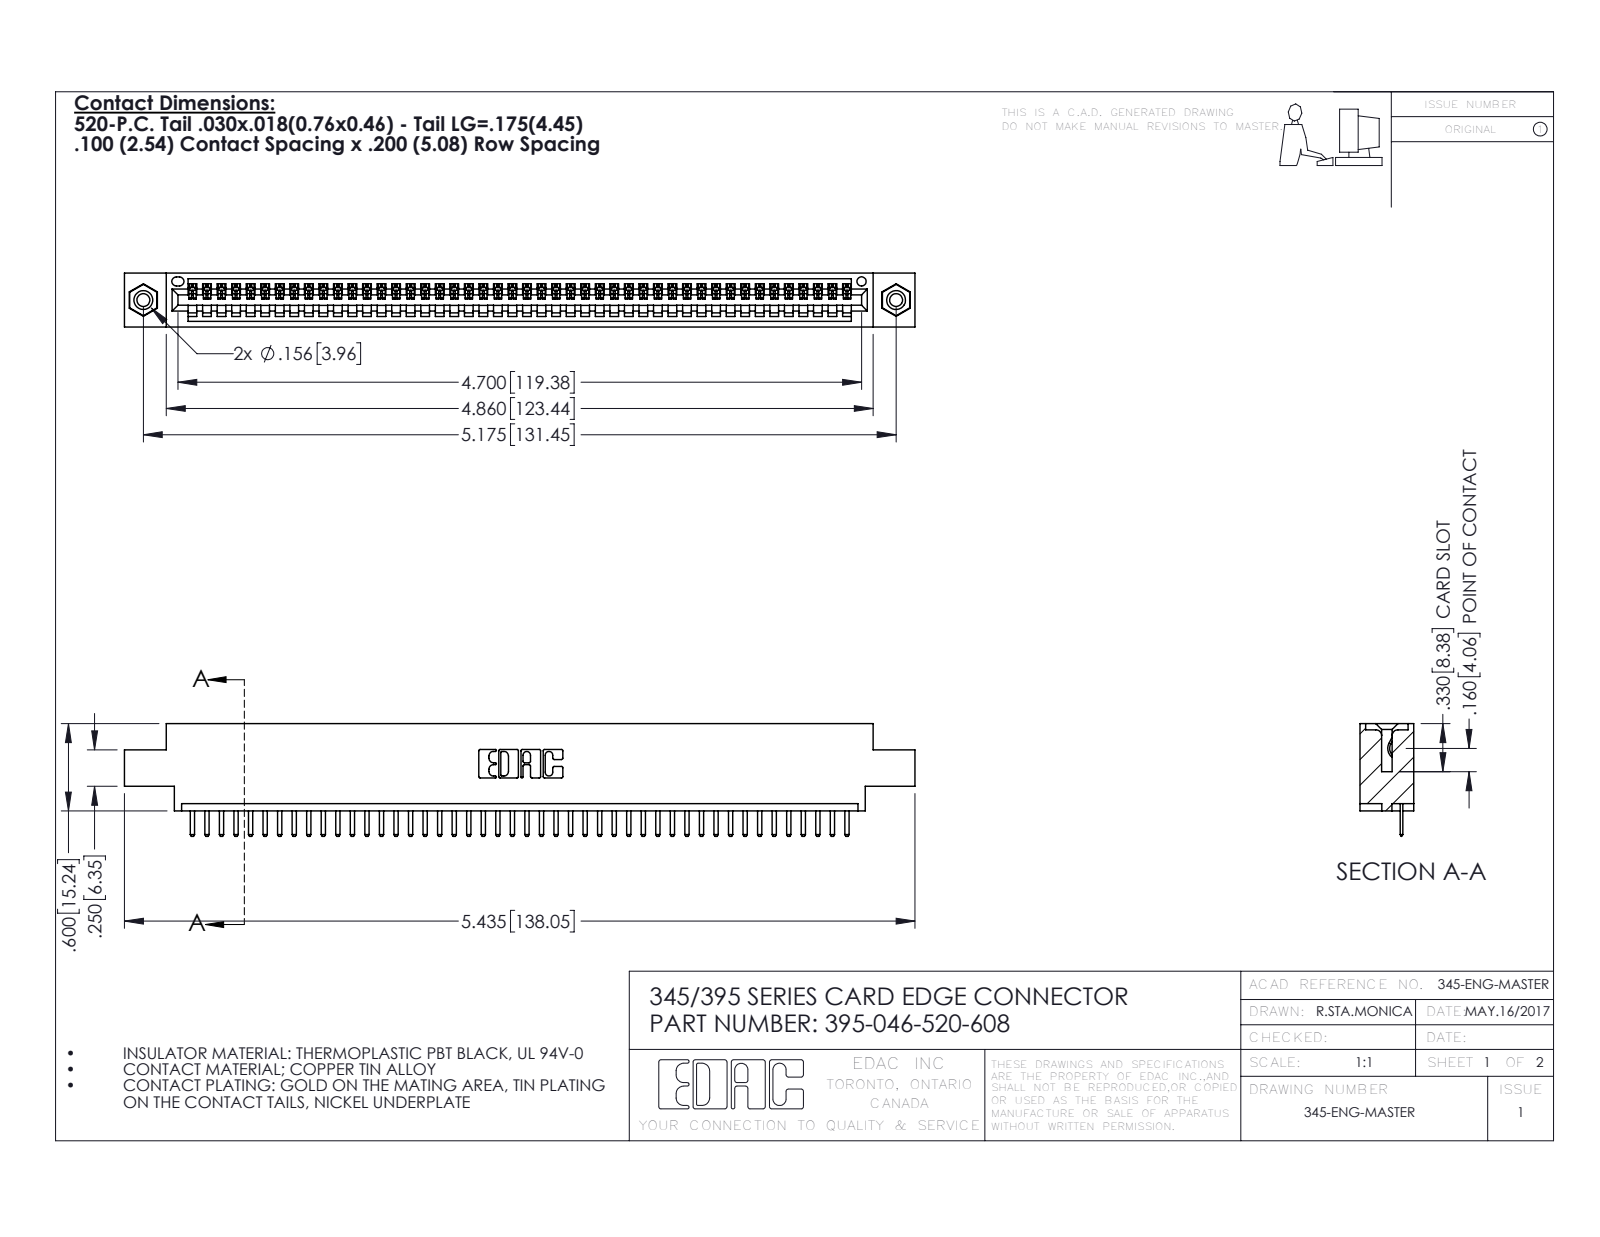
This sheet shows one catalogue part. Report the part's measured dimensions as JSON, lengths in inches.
{"part_name": "345-250-001_345-250-003-102; 395-046-520-608; 345 Part_0.170 Offset - 0.156 Dia-TI; 345-292-001_345-293-120", "step_written_by": "SolidWorks 2016 (CONFIG_CONTROL_DESIGN)", "units": "inches", "bodies": {"solids": 49, "faces": 3042, "planar": 2048, "cylindrical": 978, "other": 16}, "overall_size": [5.435, 0.775, 0.37], "volume_in3": 0.787, "surface_area_in2": 26.2, "round_holes": [[0.089, 2], [0.125, 2], [0.156, 2], [0.064, 1]], "round_bosses_or_shafts": [[0.155, 2]], "partial_cylinders_radius": [[0.01, 94], [0.006, 92], [0.01, 22], [0.007, 6], [0.031, 6], [0.026, 3], [0.031, 2], [0.04, 2]], "face_to_face_distances": [0.072, 0.298, 0.37, 0.2, 0.098, 0.272, 0.025, 0.225, 0.072, 0.175], "hole_center_spacings": [0.27, 4.939, 5.175]}
